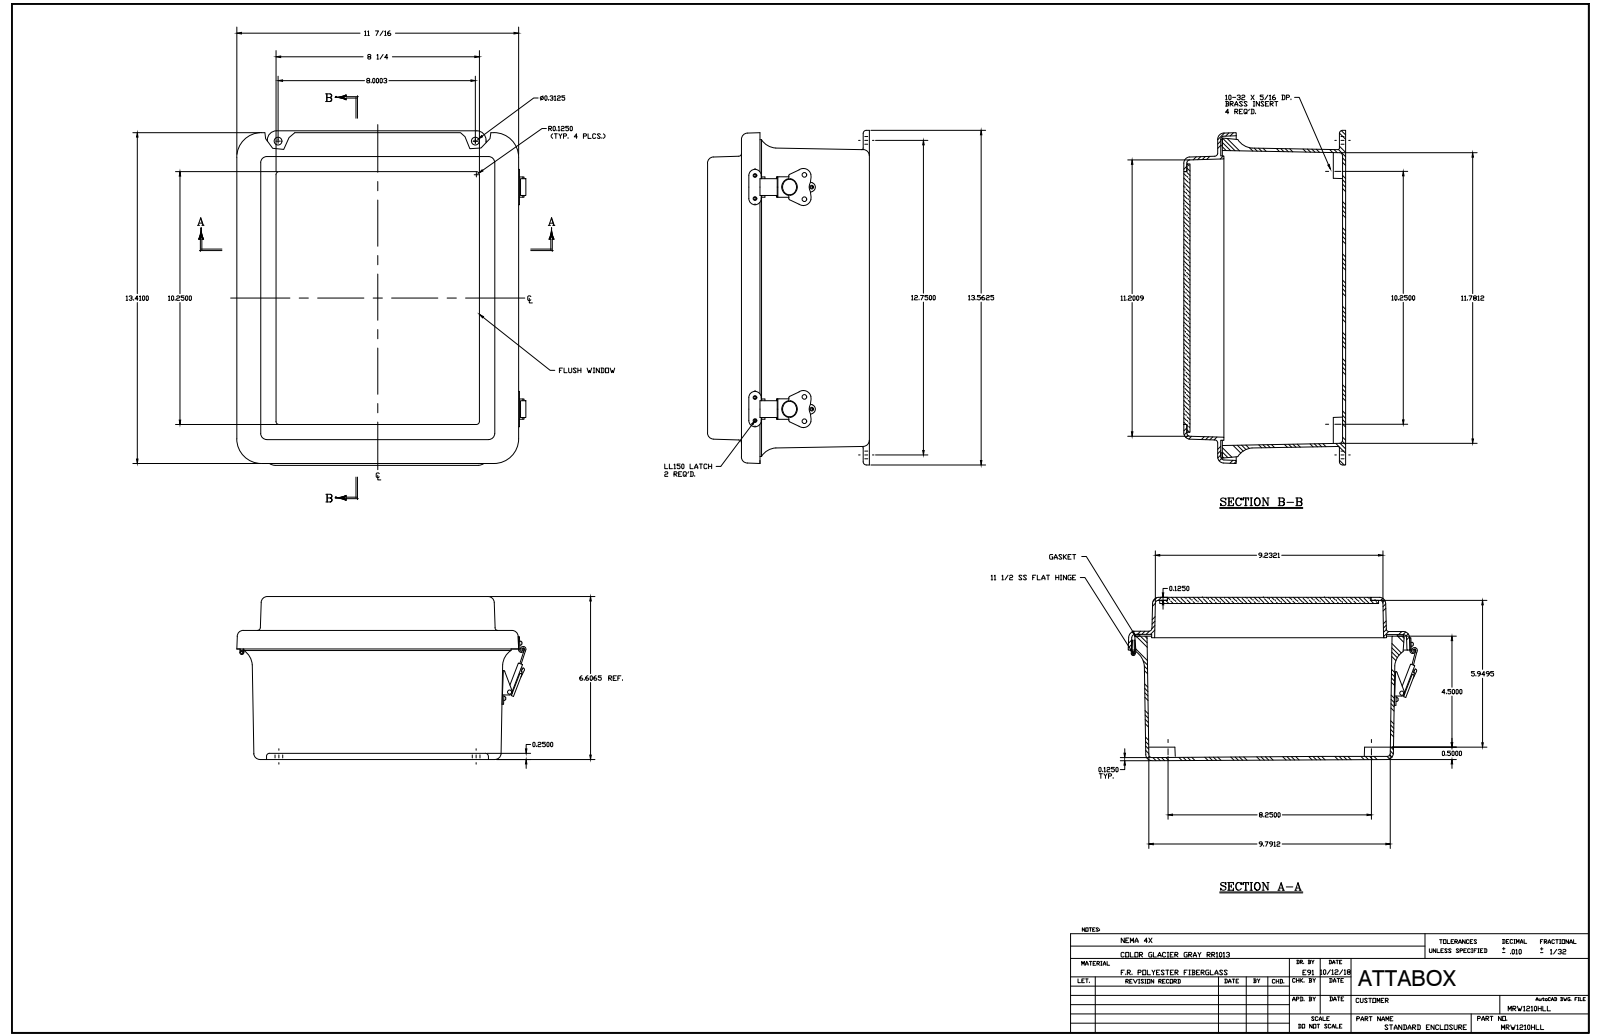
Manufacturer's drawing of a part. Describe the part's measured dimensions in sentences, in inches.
The part is named "MRW1210HLL". Its 3-D file was written by "SolidWorks 2018 (AUTOMOTIVE_DESIGN)". It is 49 solids with 1235 faces: 547 planar, 473 cylindrical and 215 other. Overall it measures 13.563 by 11.61 by 6.588 inches. Its volume is 104.2 cubic inches and its surface area 1 344 square inches. Round holes: 16 of diameter 0.14, 8 of diameter 0.131, 5 of diameter 0.152, 4 of diameter 0.13, 4 of diameter 0.156, 4 of diameter 0.165, 4 of diameter 0.197, 4 of diameter 0.218, 2 of diameter 0.118, 2 of diameter 0.138, 2 of diameter 0.181, 2 of diameter 0.182. Round bosses or shafts: 16 of diameter 0.25, 12 of diameter 0.125, 4 of diameter 0.27, 4 of diameter 0.125, 2 of diameter 0.583, 2 of diameter 0.524, 2 of diameter 0.209, 2 of diameter 0.185. Partial cylindrical surfaces (rounded edges, fillets, slot ends): 24 of radius 0.125, 20 of radius 0.031, 20 of radius 0.25, 19 of radius 0.079, 8 of radius 0.037, 8 of radius 0.039, 8 of radius 0.045, 8 of radius 0.047. The main face-to-face distances are 0.125, 6.463, 0.25, 6.338, 6.213, 6.588, 5.076, 1.387, 4.95, 1.262. The hole center spacings are 9, 3.625, 0.7, 0.938, 1.348, 1.465, 2.189, 9.031.
